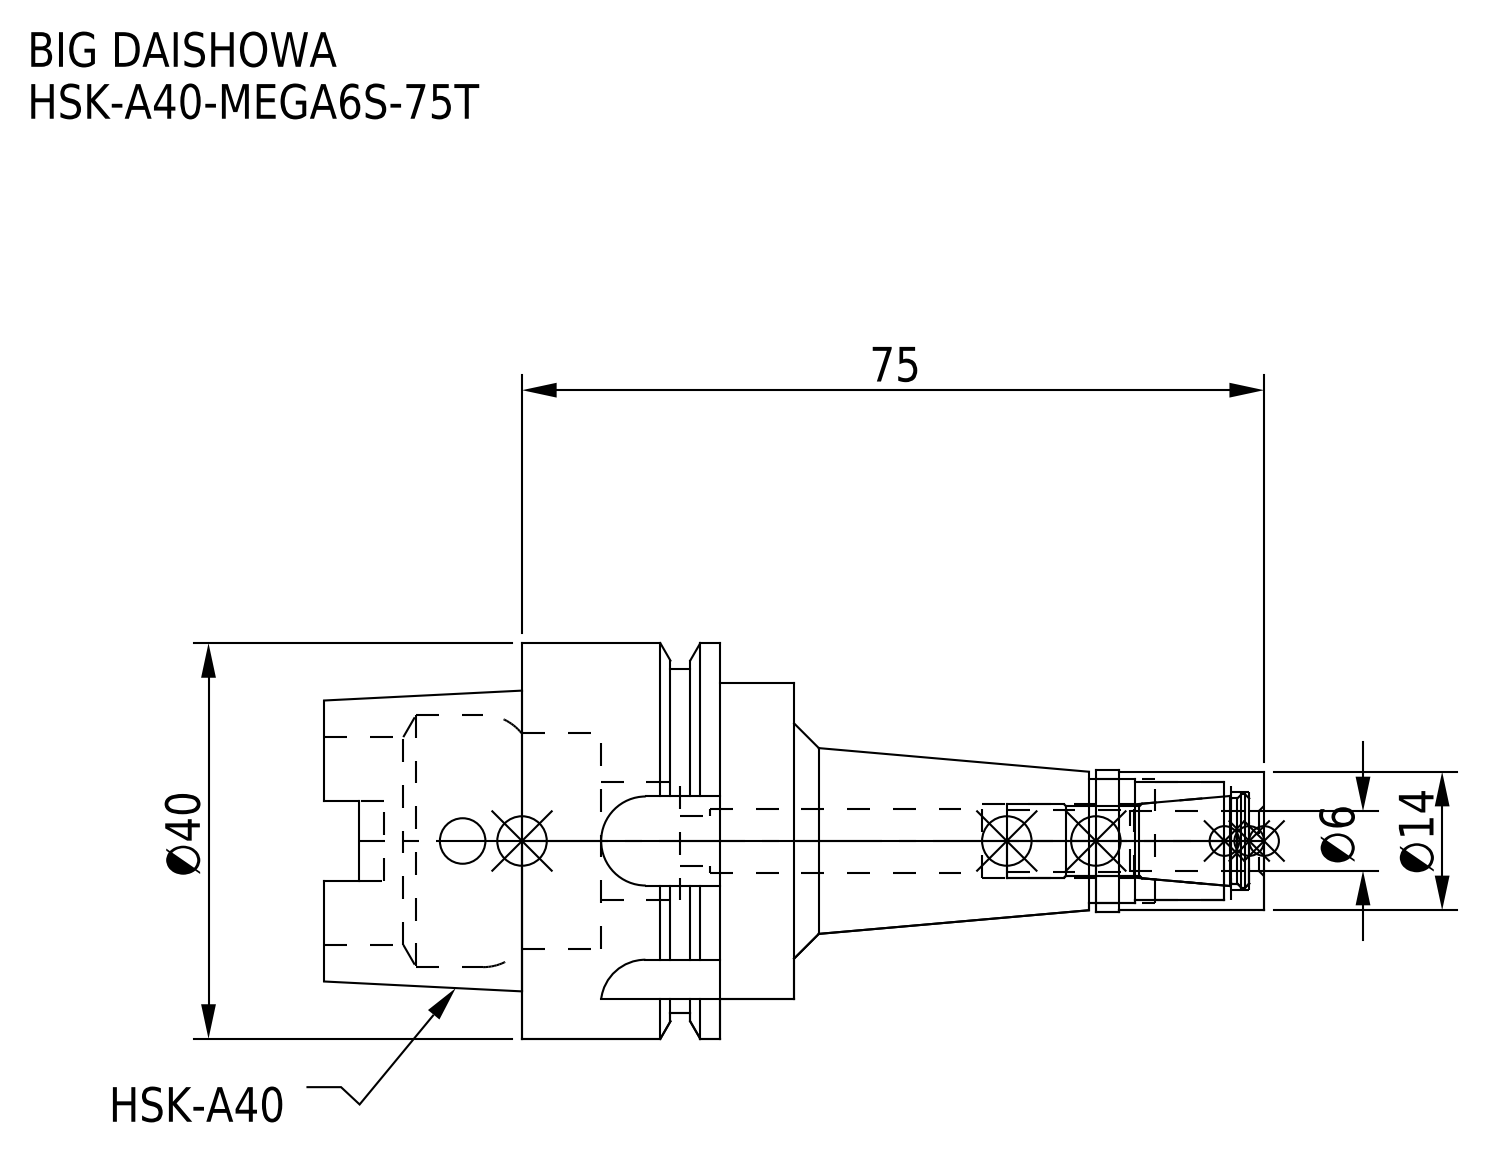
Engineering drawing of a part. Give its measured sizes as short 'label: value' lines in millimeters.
name: HA40MS06075T-060_ASM.stp; MGN6S_1.stp; HSK-A40-MEGA6S-75T-060-FreeParts; HSK-A40-MEGA6S-75T_1.stp (+3 more)
written by: SolidWorks 2019 (CONFIG_CONTROL_DESIGN)
unit: mm
bodies: 2 solids, 123 faces (47 planar, 54 cylindrical, 22 other)
size: 95 × 40 × 40
volume: 37 506 mm³; area: 14 901 mm²
holes: 1× ⌀4.6, 1× ⌀5, 1× ⌀6.1, 1× ⌀6.4, 1× ⌀7.4, 1× ⌀10, 1× ⌀12, 1× ⌀12.5, 1× ⌀21, 1× ⌀21.8, 1× ⌀25.5
bosses: 1× ⌀40, 1× ⌀34.8, 1× ⌀32, 1× ⌀14.3, 1× ⌀14
rounds: 4× R1.88, 4× R4.5
face distances: 20, 7.5, 27.5, 47.5, 19.55, 12.05, 7.95, 40, 27.95, 34
